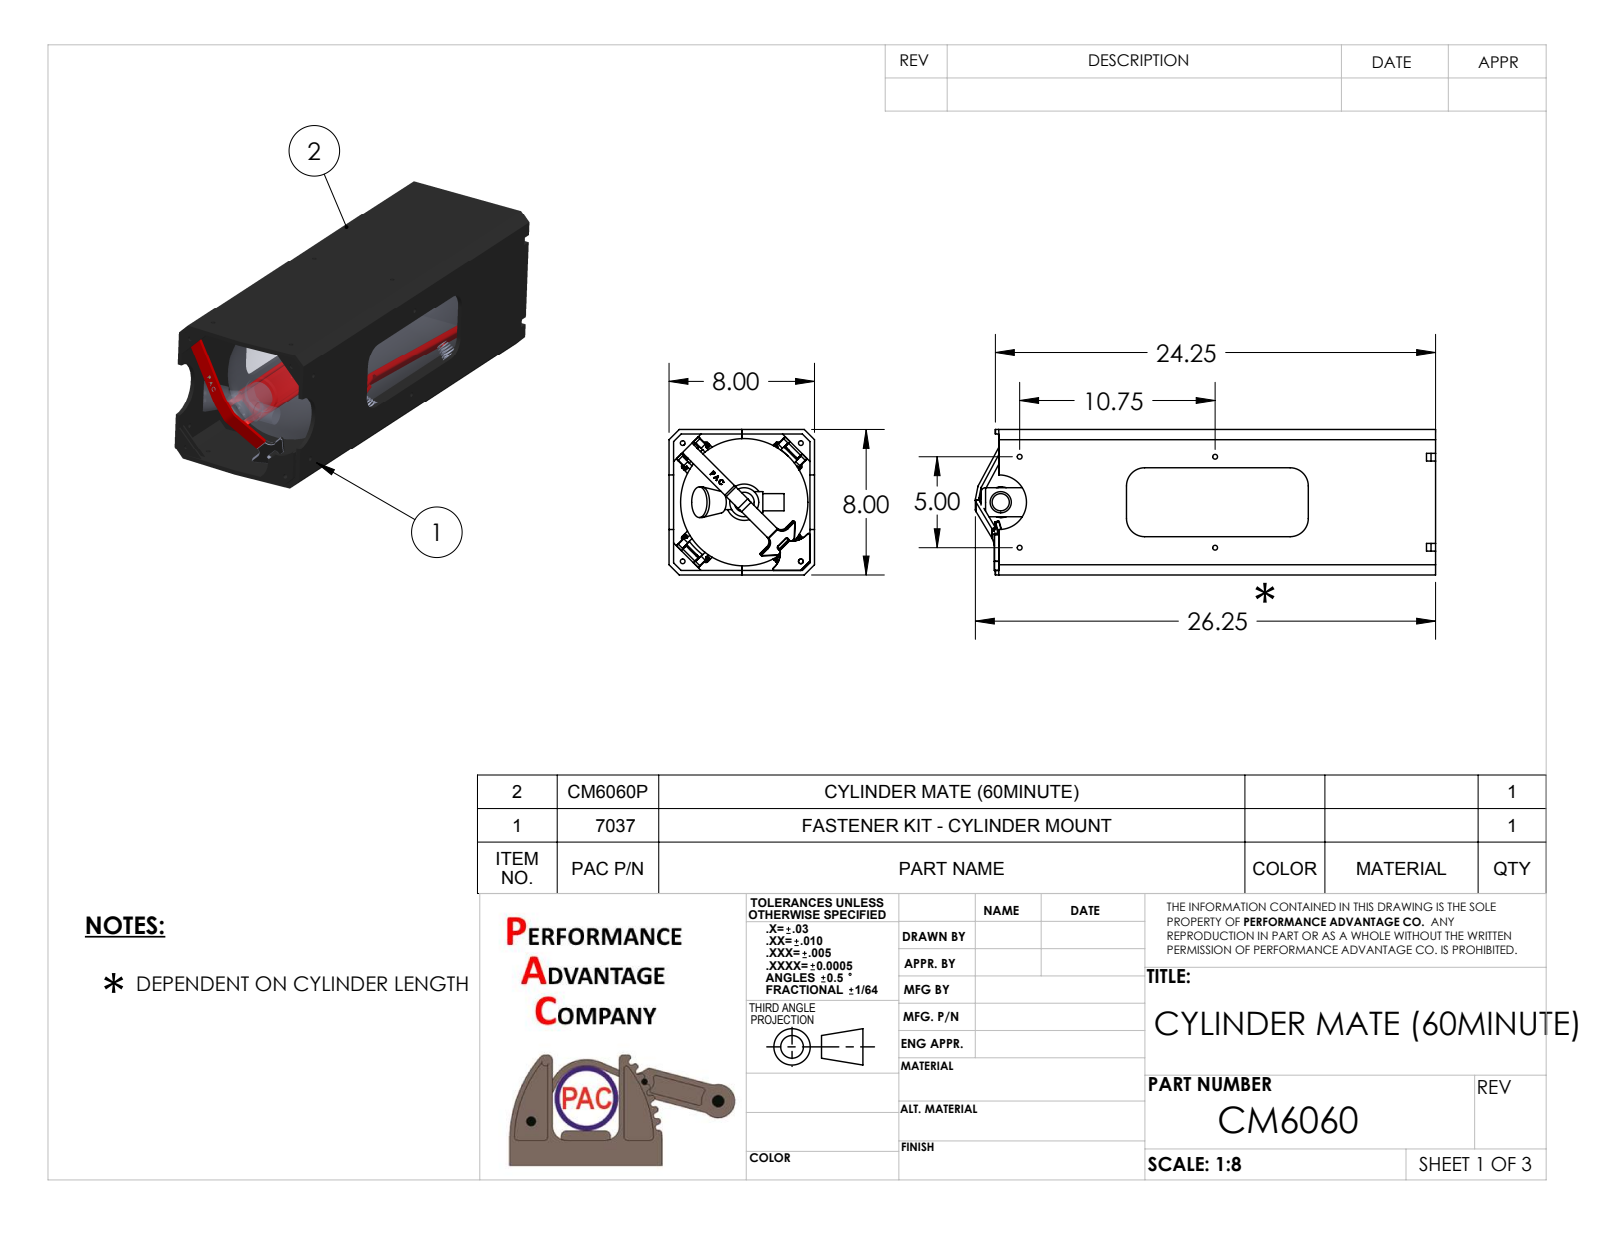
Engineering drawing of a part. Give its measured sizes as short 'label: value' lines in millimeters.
name: CM-60; CM-60 (in use); CM6000P -HOOK; guide clamp (+8 more)
written by: SolidWorks 2014 (CONFIG_CONTROL_DESIGN)
unit: mm
bodies: 55 solids, 2538 faces (704 planar, 684 cylindrical, 1150 other)
size: 642.9 × 228.6 × 215.9
volume: 16 960 000 mm³; area: 1 619 000 mm²
holes: 9× ⌀6.8, 8× ⌀4.5, 8× ⌀5.1, 8× ⌀16.3, 4× ⌀6.6
bosses: 8× ⌀14.9, 8× ⌀9.5, 4× ⌀10, 4× ⌀9.9, 4× ⌀6, 1× ⌀177.8, 1× ⌀76.2, 1× ⌀50.8
rounds: 160× R0.4, 86× R0.8, 53× R3.2, 17× R1.6, 16× R1.6, 10× R6.4, 4× R10.2, 4× R12.3
face distances: 6.4, 196.9, 203.2, 190.5, 26, 241.1, 101.6, 95.3, 215.2, 267.1
hole spacings: 127, 165.1, 273.1, 301.1, 11.1, 11.3, 233.5, 6
